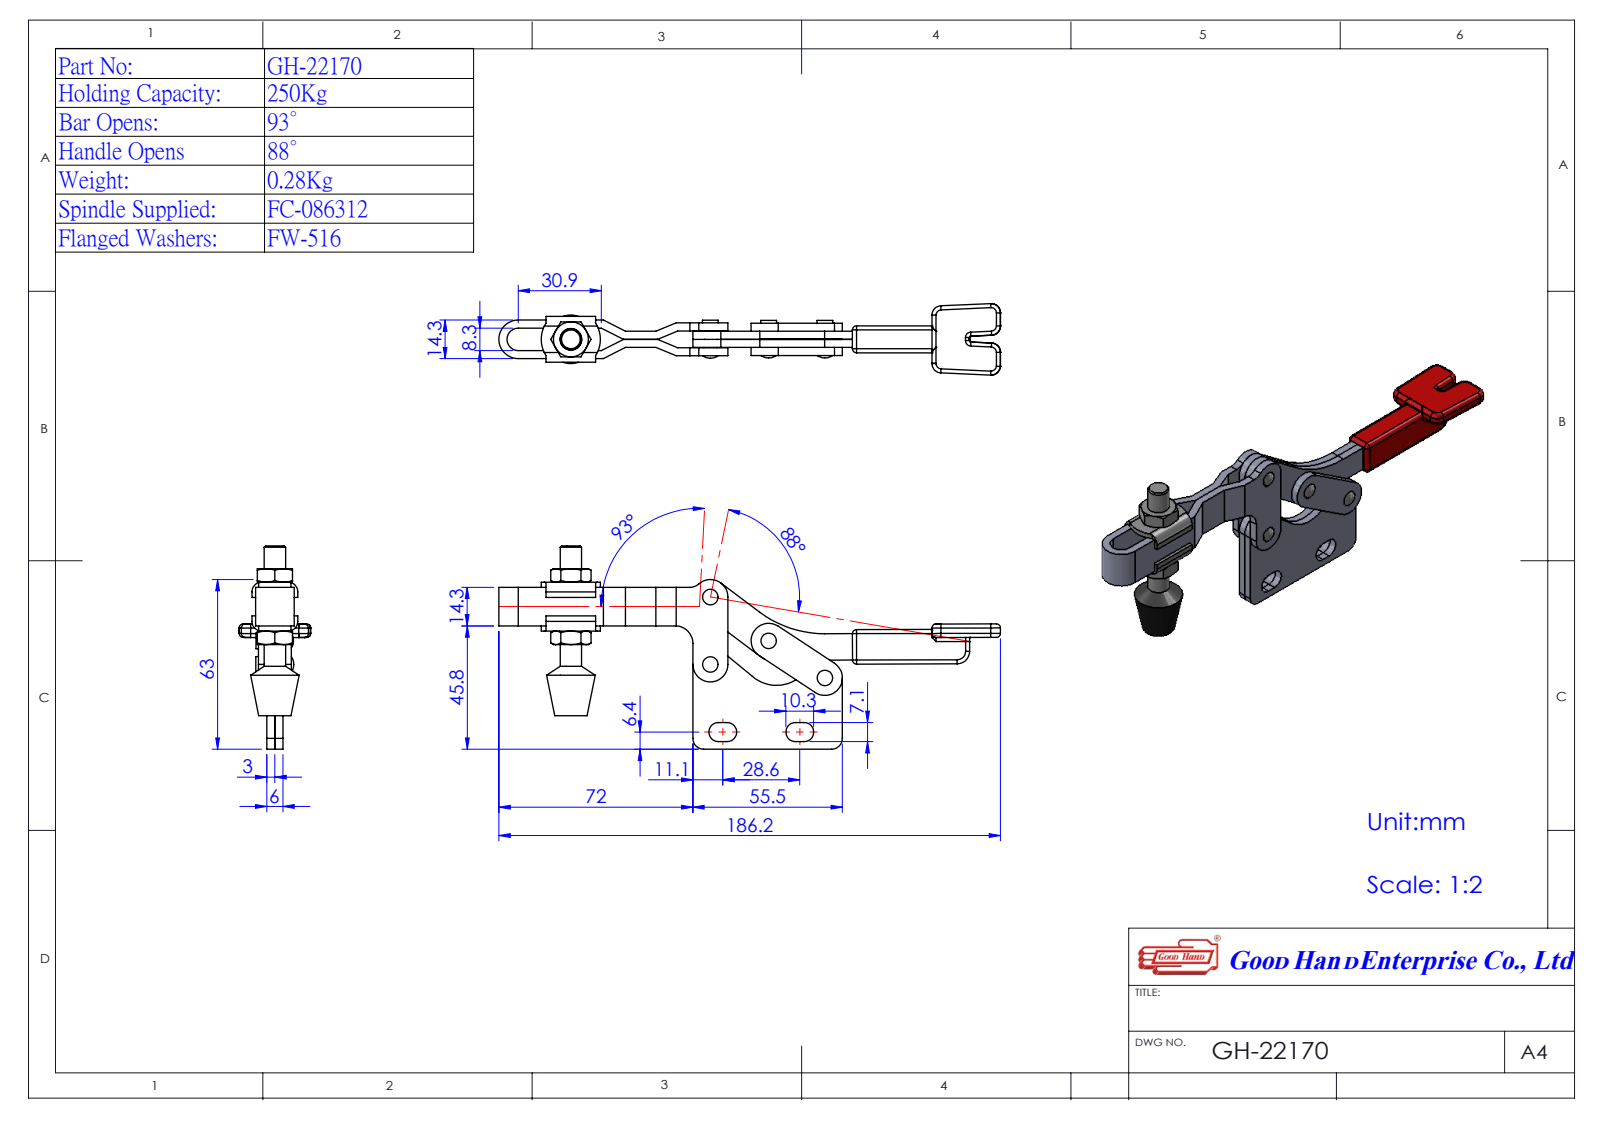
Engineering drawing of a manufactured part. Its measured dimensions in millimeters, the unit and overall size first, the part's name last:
Units: millimetres
Overall size (bounding box): 186.2 × 75.45 × 26.54
Round holes (diameter × count): ⌀3.5 ×4, ⌀4.83 ×2
Round bosses / shafts (diameter × count): ⌀5.85 ×4, ⌀13 ×1, ⌀7.93 ×1
Partial cylindrical surfaces — rounded edges, fillets, slot ends (radius × count): R3.47 ×6, R3.55 ×4, R3.6 ×4, R6.5 ×4, R0.53 ×2, R4 ×2, R5 ×2, R11.04 ×2
Main face-to-face distances: 3, 6, 3.1, 6.1, 4.15, 7.15, 10.15, 10.25, 1.05, 9.1
Hole centre spacings: 25, 23.34, 27.05, 42.79, 52.02
Volume: 41 689 mm³ · Surface area: 26 734 mm²
Bodies: 6 solids, 290 faces (146 planar, 106 cylindrical, 38 other)
Part name (STEP PRODUCT): Group1^GH-22170(簡化); Group3^GH-22170(簡化)-1; Group5^GH-22170(簡化)-1; GH-22170(簡化)-1 (+2 more)
STEP written by: SolidWorks 2016 (AUTOMOTIVE_DESIGN)
